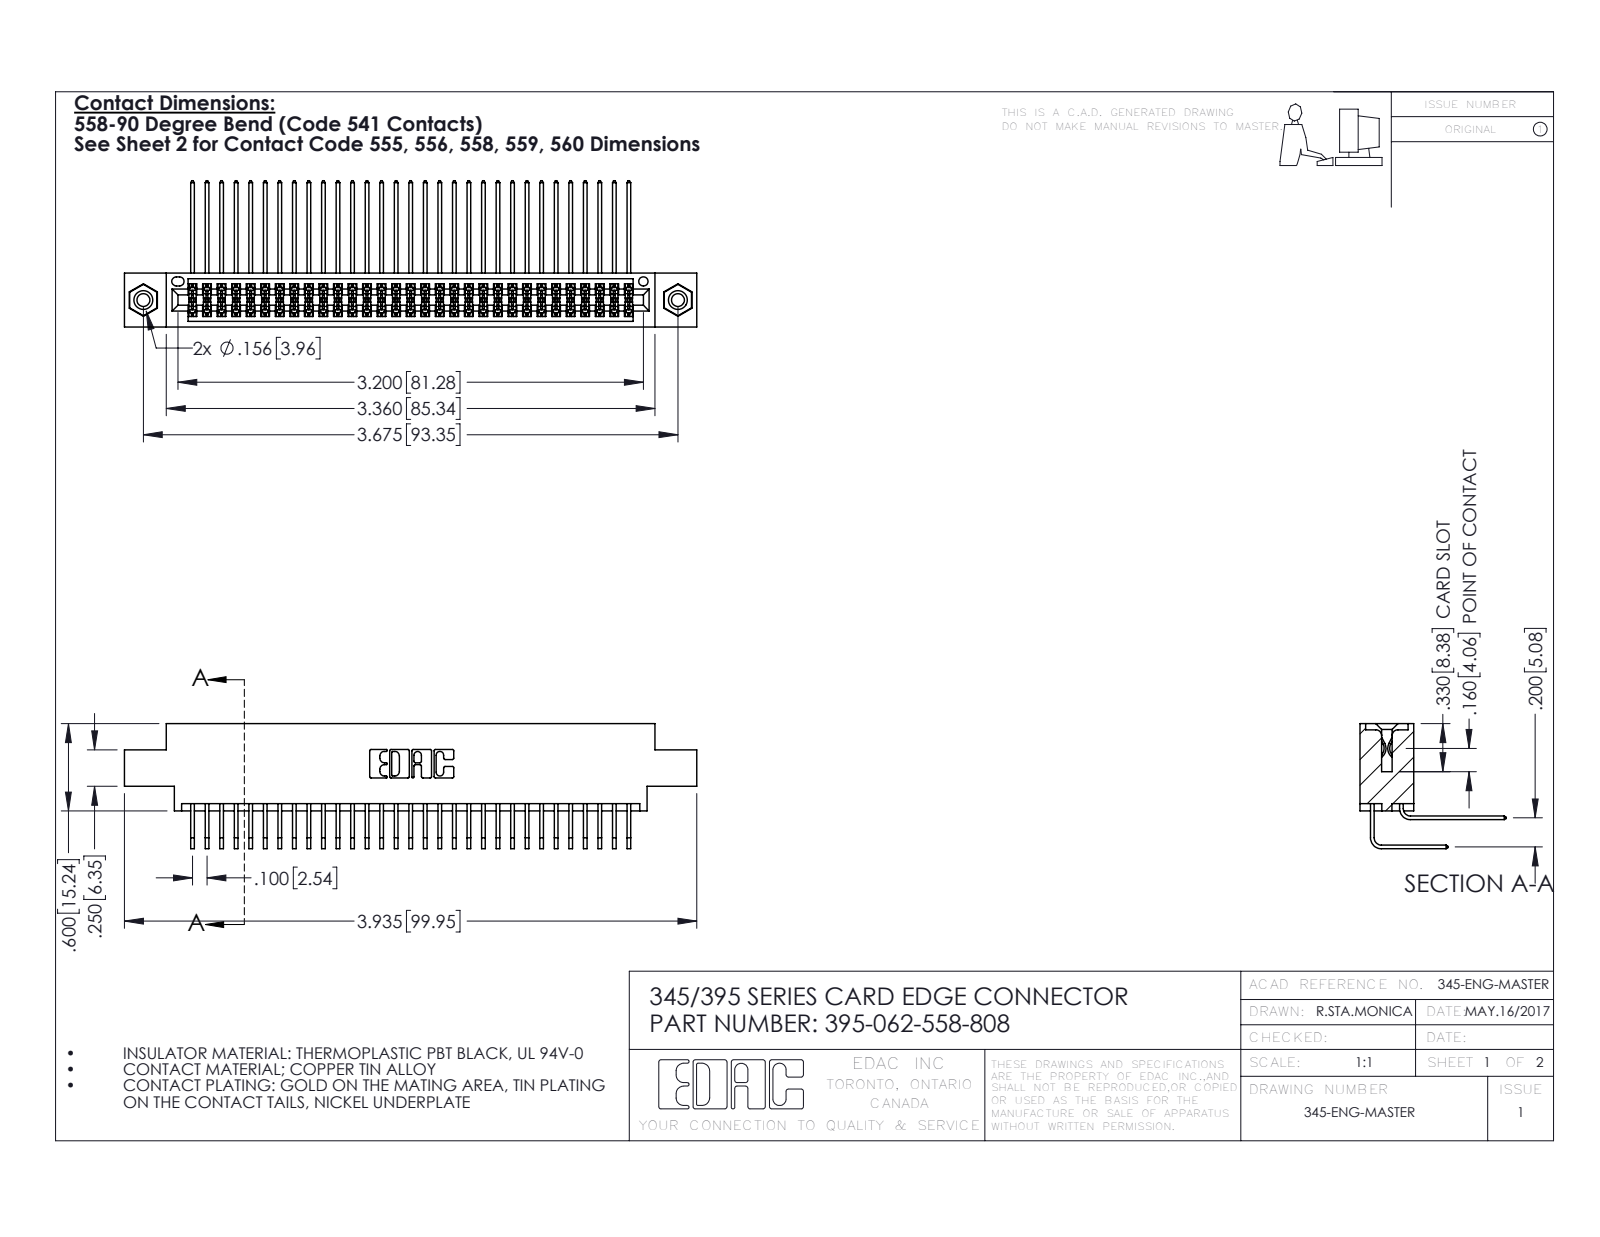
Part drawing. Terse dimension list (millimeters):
name: 345-292-001_558 Tail - 2; 345 Part_0.170 Offset - 0.156 Dia-TI; 345-292-001_558 559 Tail - 1; 395-062-558-808 (+1 more)
written by: SolidWorks 2016 (CONFIG_CONTROL_DESIGN)
unit: mm
bodies: 65 solids, 3414 faces (2286 planar, 1112 cylindrical, 16 other)
size: 99.9 × 25.5 × 21.8
volume: 9 850 mm³; area: 16 180 mm²
holes: 2× ⌀2.3, 2× ⌀3.2, 2× ⌀4, 1× ⌀1.6
bosses: 2× ⌀3.9
rounds: 94× R0.2, 22× R0.3, 6× R0.2, 6× R0.8, 3× R0.7, 2× R0.4, 2× R0.5, 2× R0.6
face distances: 1.8, 7.6, 5.1, 9.4, 2.5, 6.9, 0.6, 5.7, 4.4, 0.6
hole spacings: 6.9, 87.4, 93.3
